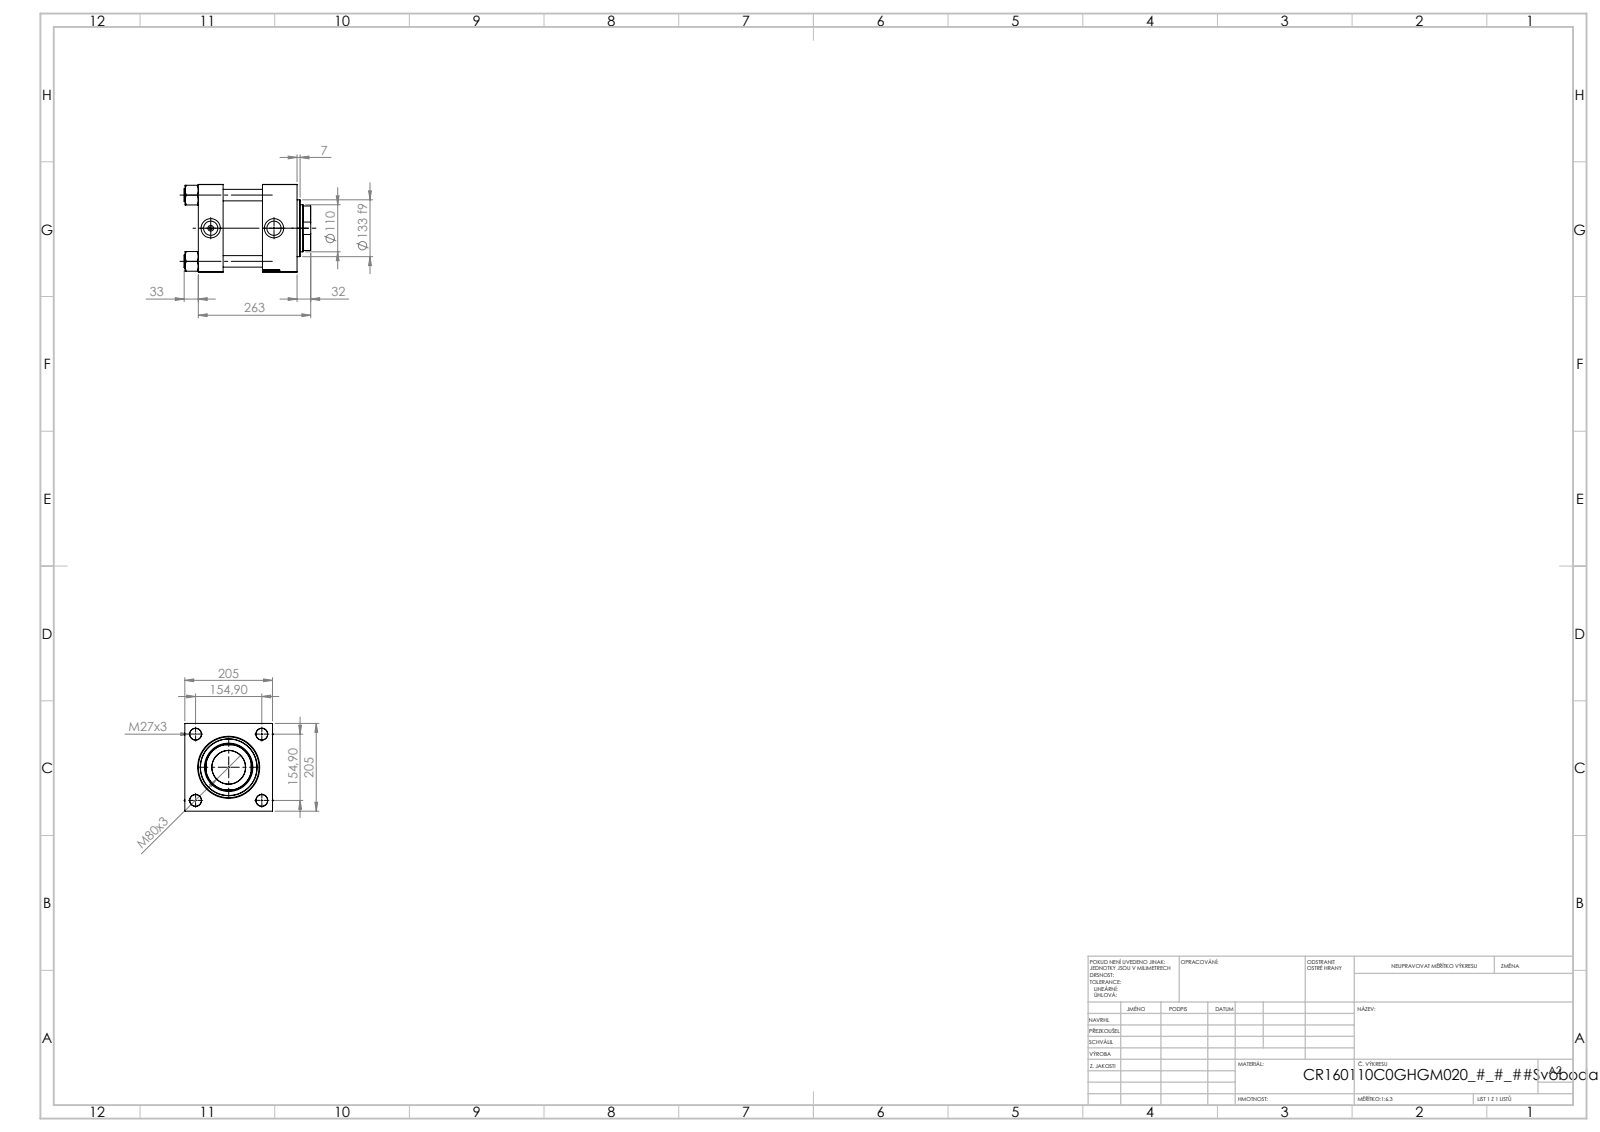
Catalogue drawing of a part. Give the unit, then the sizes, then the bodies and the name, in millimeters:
Units: millimetres
Overall size (bounding box): 296 × 208.14 × 205
Round holes (diameter × count): ⌀27 ×4, ⌀7 ×2, ⌀33.24 ×2, ⌀45 ×2, ⌀78.5 ×1, ⌀110 ×1, ⌀113 ×1, ⌀120 ×1, ⌀142 ×1, ⌀160 ×1
Round bosses / shafts (diameter × count): ⌀30 ×4, ⌀166 ×1, ⌀133 ×1
Partial cylindrical surfaces — rounded edges, fillets, slot ends (radius × count): R54 ×1
Main face-to-face distances: 205, 58, 150, 92, 231, 173, 81, 202.3, 144.3, 52.3
Hole centre spacings: 109.53, 154.9, 219.06, 148
Volume: 7 650 000 mm³ · Surface area: 720 256 mm²
Bodies: 11 solids, 1196 faces (574 planar, 86 cylindrical, 536 other)
Part name (STEP PRODUCT): V215CR_VCP_C; V215_VC_A; NUT_M5_C; V215CR_C_Body (+1 more)
STEP written by: SolidWorks 2019 (CONFIG_CONTROL_DESIGN)
